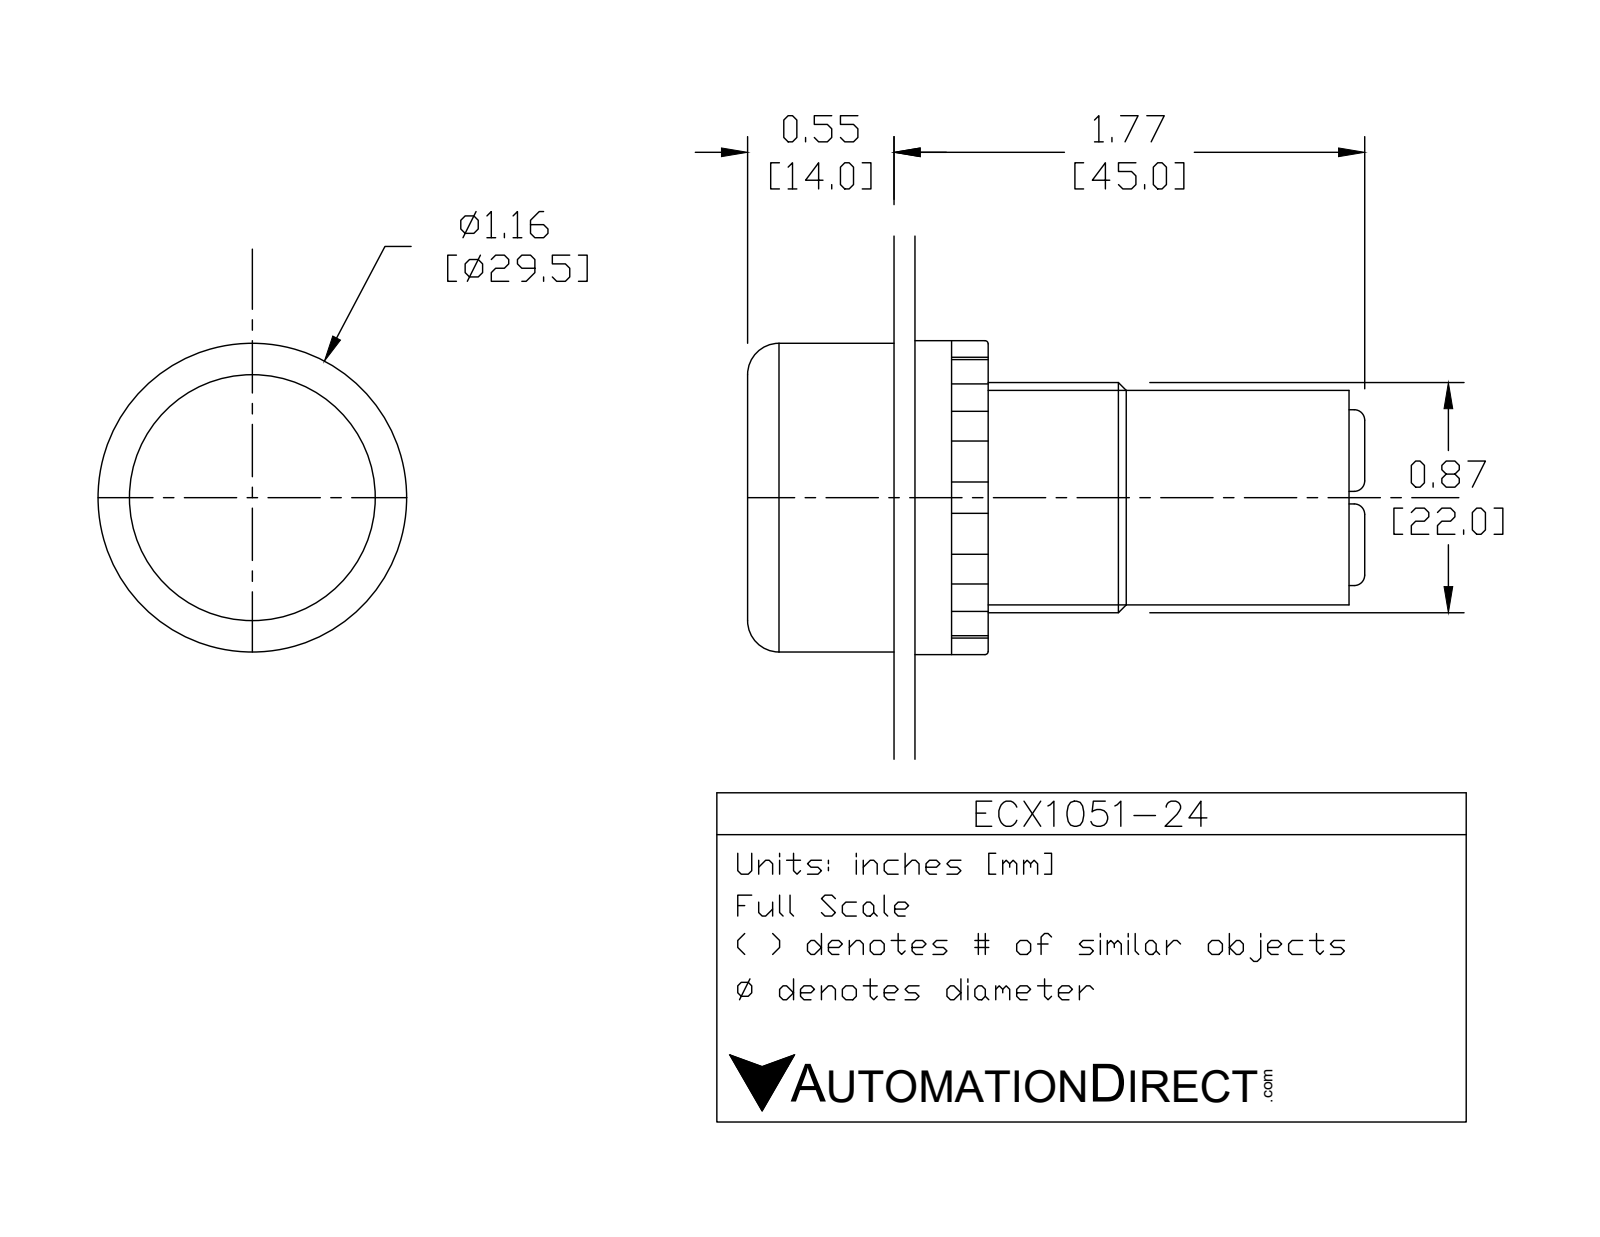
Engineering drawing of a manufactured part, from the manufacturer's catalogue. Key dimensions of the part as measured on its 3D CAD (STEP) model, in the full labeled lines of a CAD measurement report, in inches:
Part name (STEP PRODUCT): ECX1051-24
STEP written by: SolidWorks 2017 (AUTOMOTIVE_DESIGN)
Units: inches
Bodies: 6 solids, 125 faces (63 planar, 41 cylindrical, 21 other)
Overall size (bounding box): 2.323 × 1.181 × 1.181
Volume: 1.605 in³ · Surface area: 15.04 in²
Round holes (diameter × count): ⌀0.217 ×2, ⌀0.886 ×1
Round bosses / shafts (diameter × count): ⌀0.157 ×2, ⌀1.181 ×1, ⌀1.142 ×1, ⌀1.043 ×1, ⌀0.866 ×1, ⌀0.787 ×1
Partial cylindrical surfaces — rounded edges, fillets, slot ends (radius × count): R0.039 ×12, R0.354 ×1
Main face-to-face distances: 0.531, 0.02, 0.551, 0.787, 0.236, 0.256, 1.535, 0.276, 0.512, 1.063
Hole centre spacings: 0.182, 0.364
